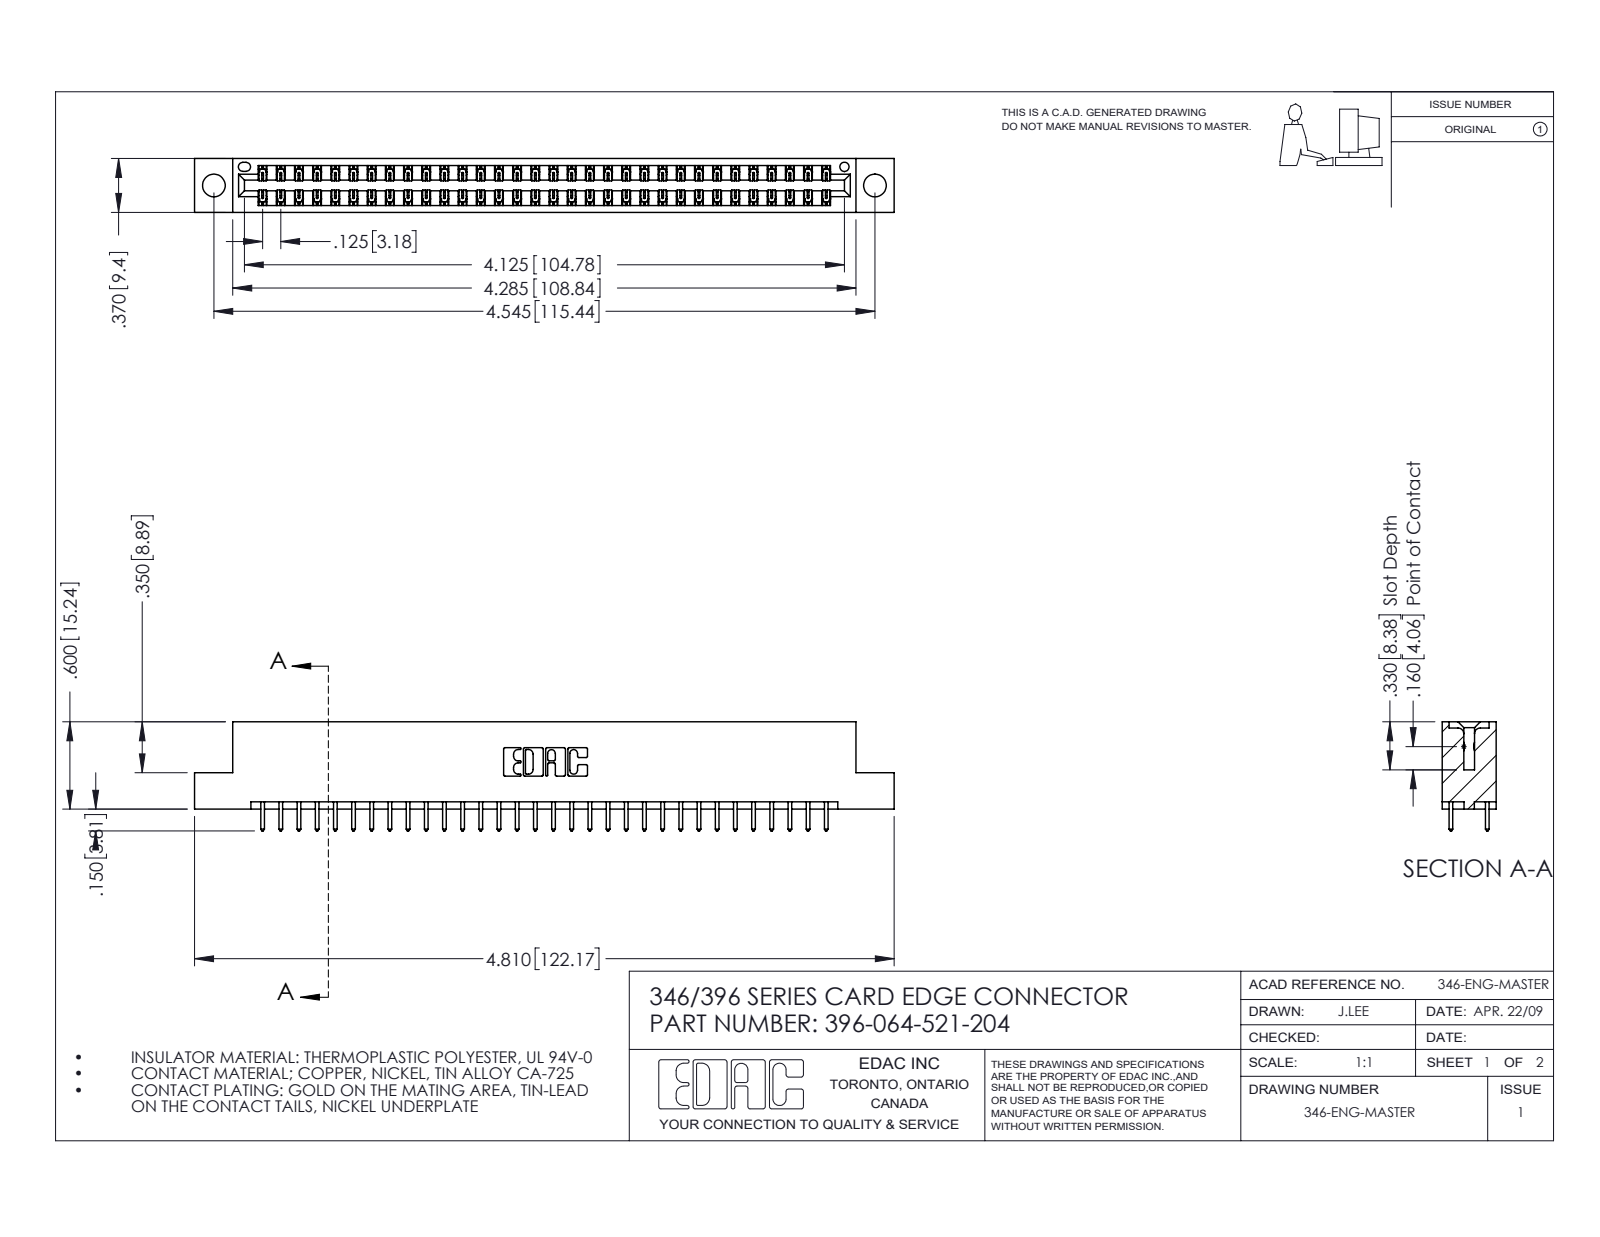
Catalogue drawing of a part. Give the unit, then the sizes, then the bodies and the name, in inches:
Units: inches
Overall size (bounding box): 4.81 × 0.75 × 0.37
Round holes (diameter × count): ⌀0.156 ×2, ⌀0.064 ×1
Partial cylindrical surfaces — rounded edges, fillets, slot ends (radius × count): R0.006 ×96, R0.01 ×64, R0.01 ×22, R0.007 ×6, R0.031 ×6, R0.026 ×3, R0.014 ×2, R0.022 ×2
Main face-to-face distances: 0.048, 0.322, 0.25, 0.37, 0.072, 0.298, 0.025, 0.275, 0.148, 0.222
Hole centre spacings: 0.246, 4.337, 4.545
Volume: 0.715 in³ · Surface area: 24.17 in²
Bodies: 65 solids, 3450 faces (2316 planar, 1134 cylindrical, 0 other)
Part name (STEP PRODUCT): 346 Part_Flush Mounting Lugs - 0.156 Dia-TH; 345-292-001_345-293-121; 396-064-521-204
STEP written by: SolidWorks 2016 (CONFIG_CONTROL_DESIGN)
